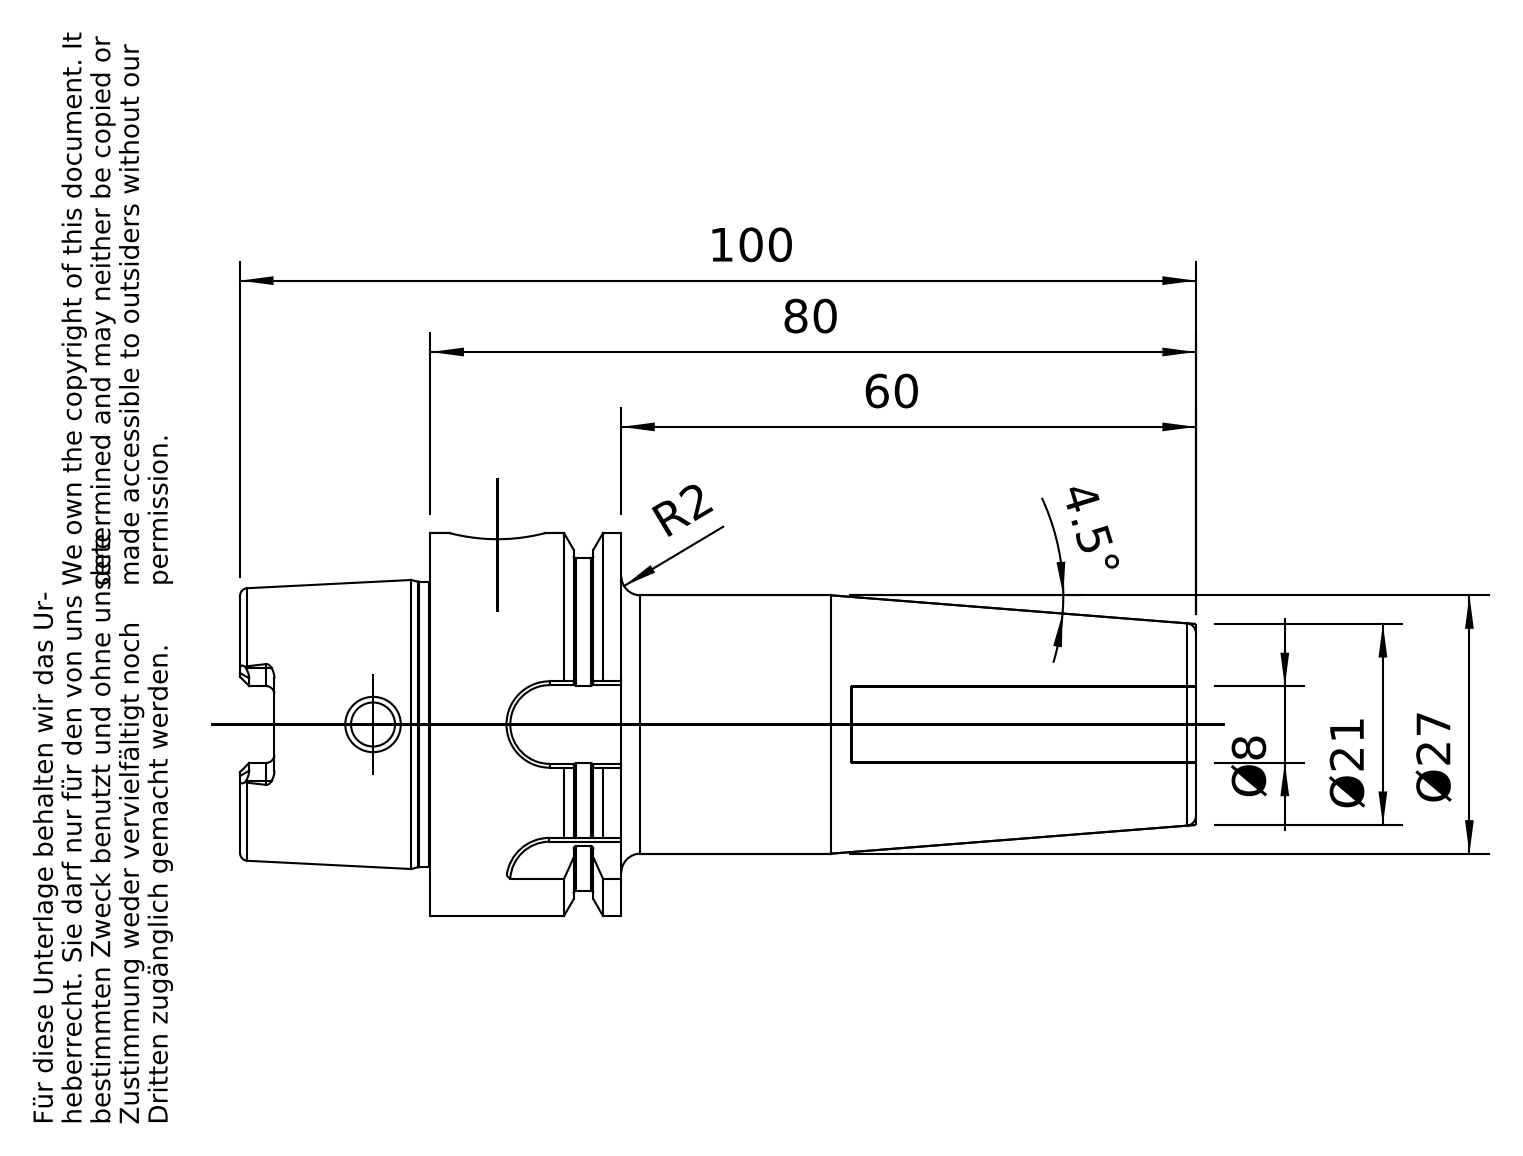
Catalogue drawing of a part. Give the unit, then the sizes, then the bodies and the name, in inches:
Units: inches
Overall size (bounding box): 3.933 × 1.575 × 1.575
Round holes (diameter × count): ⌀0.181 ×1, ⌀0.315 ×1, ⌀0.394 ×1, ⌀0.402 ×1, ⌀0.472 ×1, ⌀0.481 ×1, ⌀0.492 ×1, ⌀0.828 ×1, ⌀1.007 ×1
Round bosses / shafts (diameter × count): ⌀1.575 ×1, ⌀1.368 ×1, ⌀1.174 ×1, ⌀1.063 ×1
Partial cylindrical surfaces — rounded edges, fillets, slot ends (radius × count): R0.035 ×6, R0.074 ×4, R0.177 ×3, R0.178 ×1
Main face-to-face distances: 0.785, 3.15, 2.364, 0.313, 0.472, 2.837, 0.783, 1.096, 1.569, 3.933
Volume: 3.187 in³ · Surface area: 23.35 in²
Bodies: 1 solid, 184 faces (60 planar, 50 cylindrical, 74 other)
Part name (STEP PRODUCT): A40-140-08
STEP written by: PRO/ENGINEER BY PARAMETRIC TECHNOLOGY CORPORATION, 2010430 (CONFIG_CONTROL_DESIGN)
